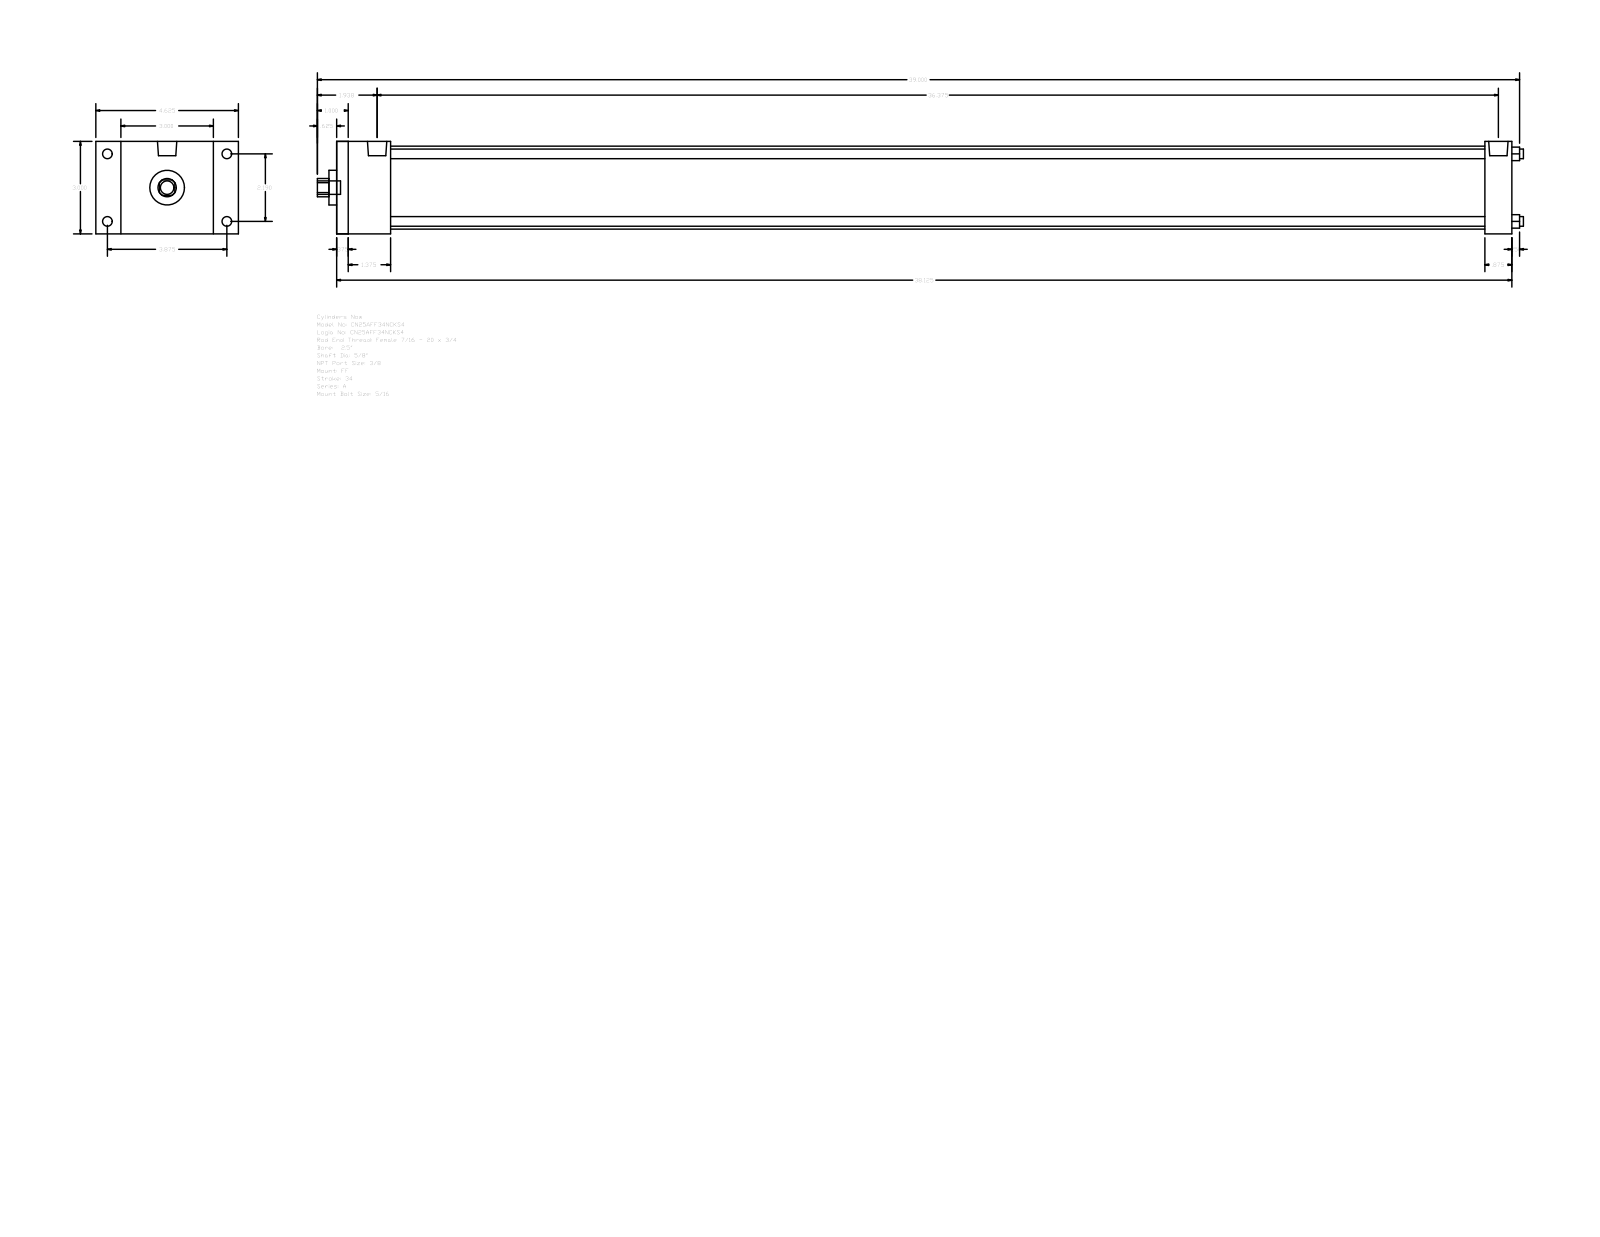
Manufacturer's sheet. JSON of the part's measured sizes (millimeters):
{"part_name": "A_FF__0250_0.625", "step_written_by": "GSSL Pune (CONFIG_CONTROL_DESIGN)", "units": "millimeters", "bodies": {"solids": 0, "faces": 92, "planar": 64, "cylindrical": 28, "other": 0}, "overall_size": [993.77, 117.47, 76.2], "round_holes": [[7.94, 4], [15.88, 1], [28.57, 1], [68.33, 1]], "round_bosses_or_shafts": [[7.94, 4], [5.56, 4], [15.93, 2], [11.11, 1]], "partial_cylinders_radius": [[7.54, 1]], "face_to_face_distances": [76.2, 968.37, 9.52, 958.85, 44.45, 946.14, 34.93, 936.62, 901.69, 923.92], "hole_center_spacings": [39.33, 55.62, 78.66]}
